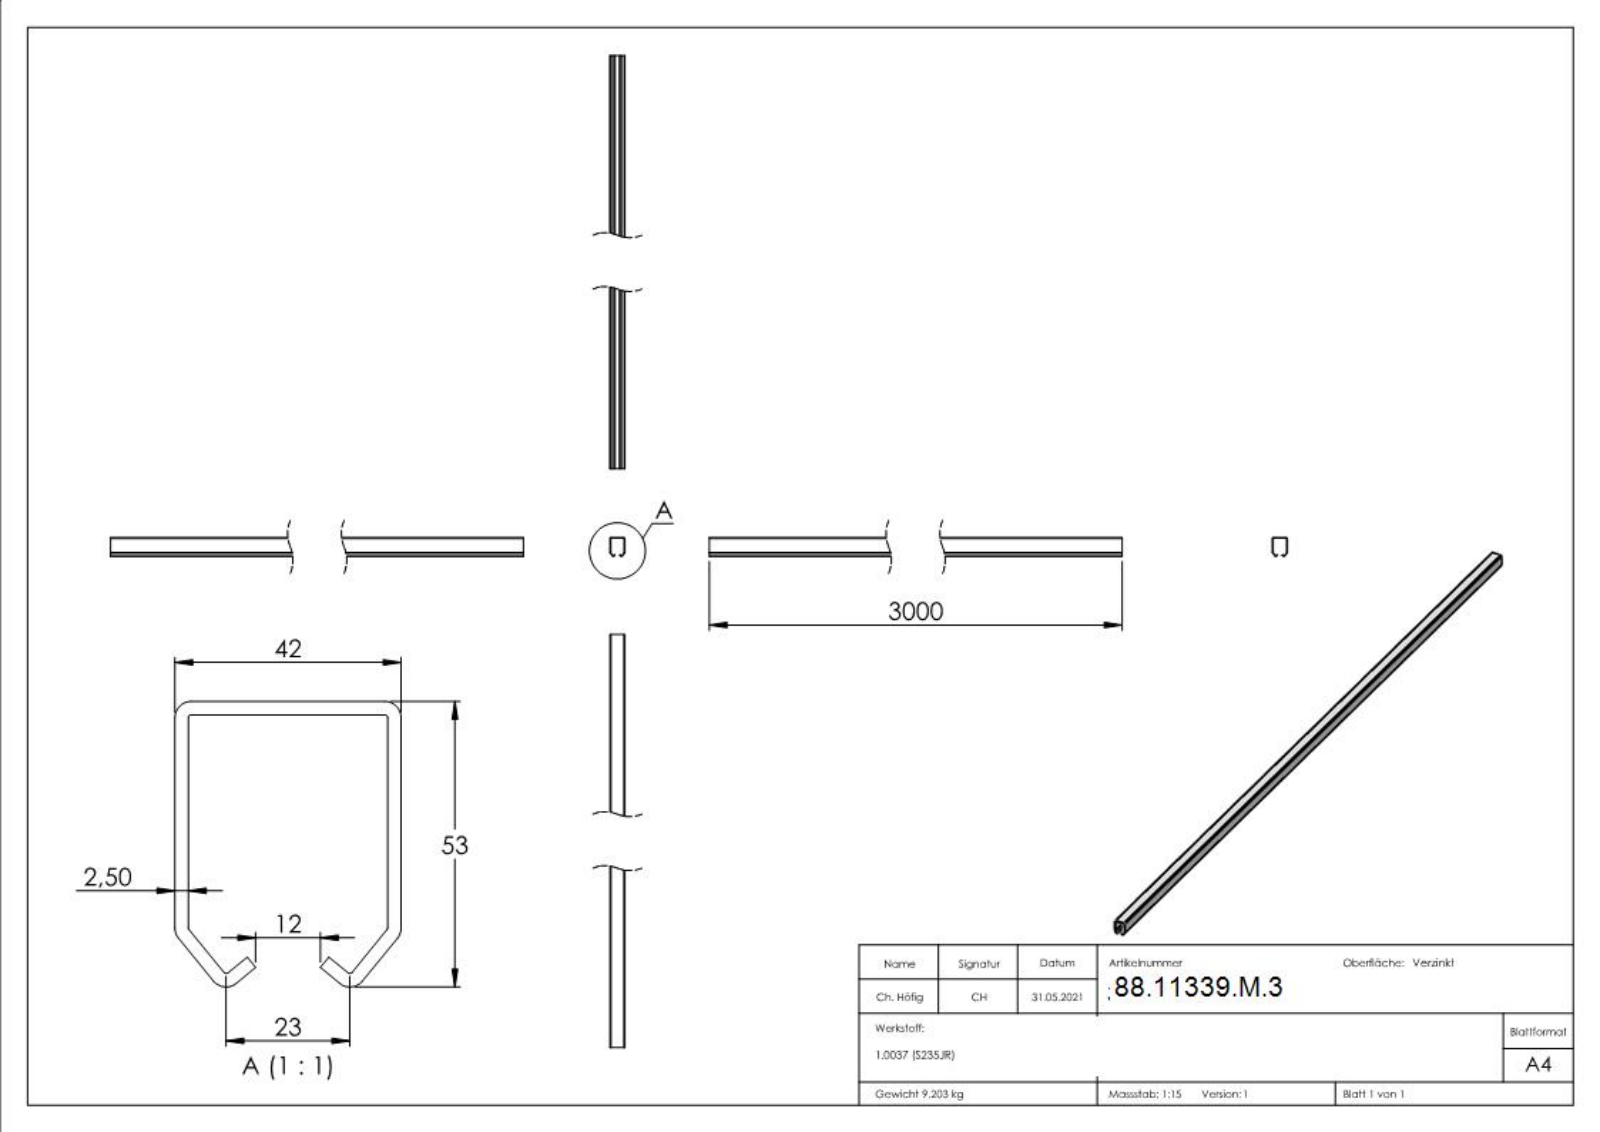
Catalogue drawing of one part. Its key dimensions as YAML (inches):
part_name: "339-M-3"
step_written_by: "SolidWorks 2018 (CONFIG_CONTROL_DESIGN)"
units: inches
bodies: {solids: 1, faces: 278, planar: 147, cylindrical: 12, other: 119}
overall_size: [118.11, 2.087, 1.654]
volume: 72.01
surface_area: 1488
partial_cylinders:
  - {radius: 0.02, count: 6}
  - {radius: 0.118, count: 6}
face_to_face_distances: [0.098, 1.555, 1.654, 1.457, 0.203, 0.302, 118.11, 0.094, 0.778, 0.045]
